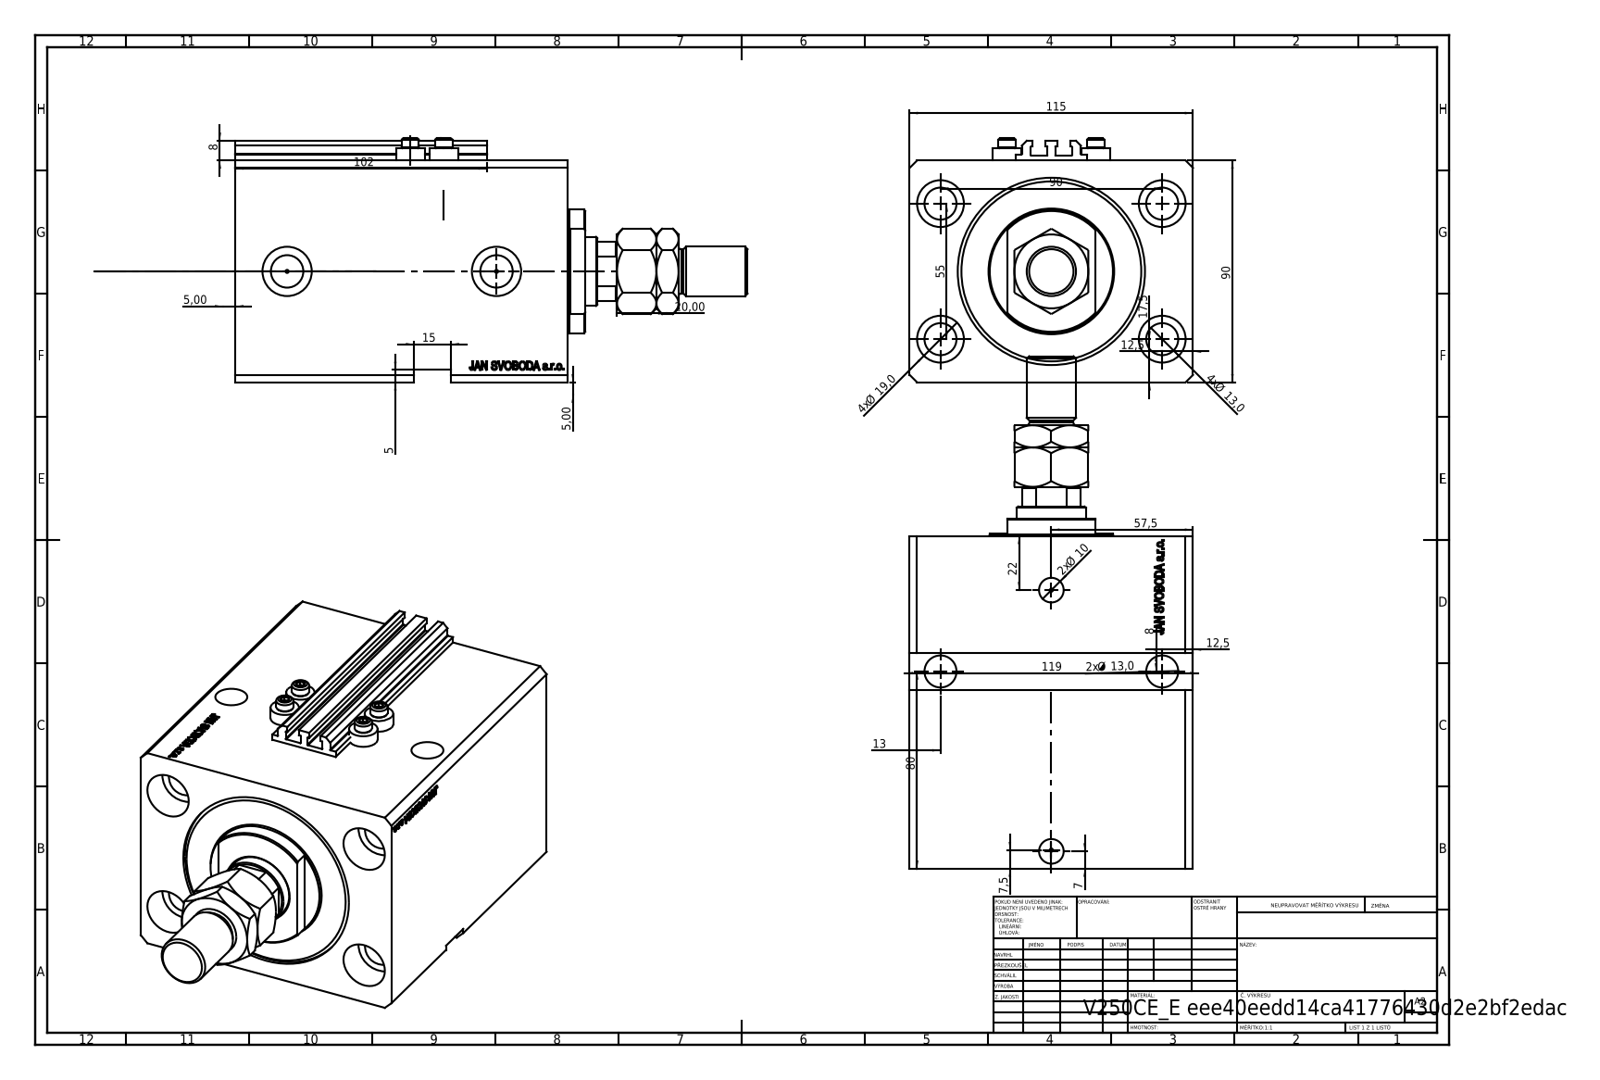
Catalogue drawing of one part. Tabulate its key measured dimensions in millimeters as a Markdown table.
| quantity | value |
| --- | --- |
| part name | MTA; V250CE_E_Body; ALLEN BOLT V250CE; V250CE_C_VCP (+1 more) |
| STEP written by | SolidWorks 2019 (CONFIG_CONTROL_DESIGN) |
| units | millimeters |
| bodies | 9 solids, 1156 faces (558 planar, 130 cylindrical, 468 other) |
| overall size | 207.9 × 115 × 99 |
| volume | 1 205 000 mm³ |
| surface area | 190 939 mm² |
| round holes (diameter × count) | 13 × 6, 1.25 × 4, 4 × 4, 19 × 4, 10 × 2, 13.16 × 2, 20 × 2, 18.5 × 1, 28 × 1, 63 × 1, 76 × 1 |
| round bosses / shafts (diameter × count) | 11.6 × 4, 7 × 4, 50 × 1, 20 × 1, 18 × 1 |
| partial cylindrical surfaces (radius × count) | 0.2 × 10, 13.5 × 1 |
| main face-to-face distances | 90, 115, 135, 87, 17.9, 117.1, 104.9, 30.1, 50, 54.9 |
| hole center spacings | 52.74, 90, 13.6, 27.39, 28.46, 33.62, 36, 38.48 |
